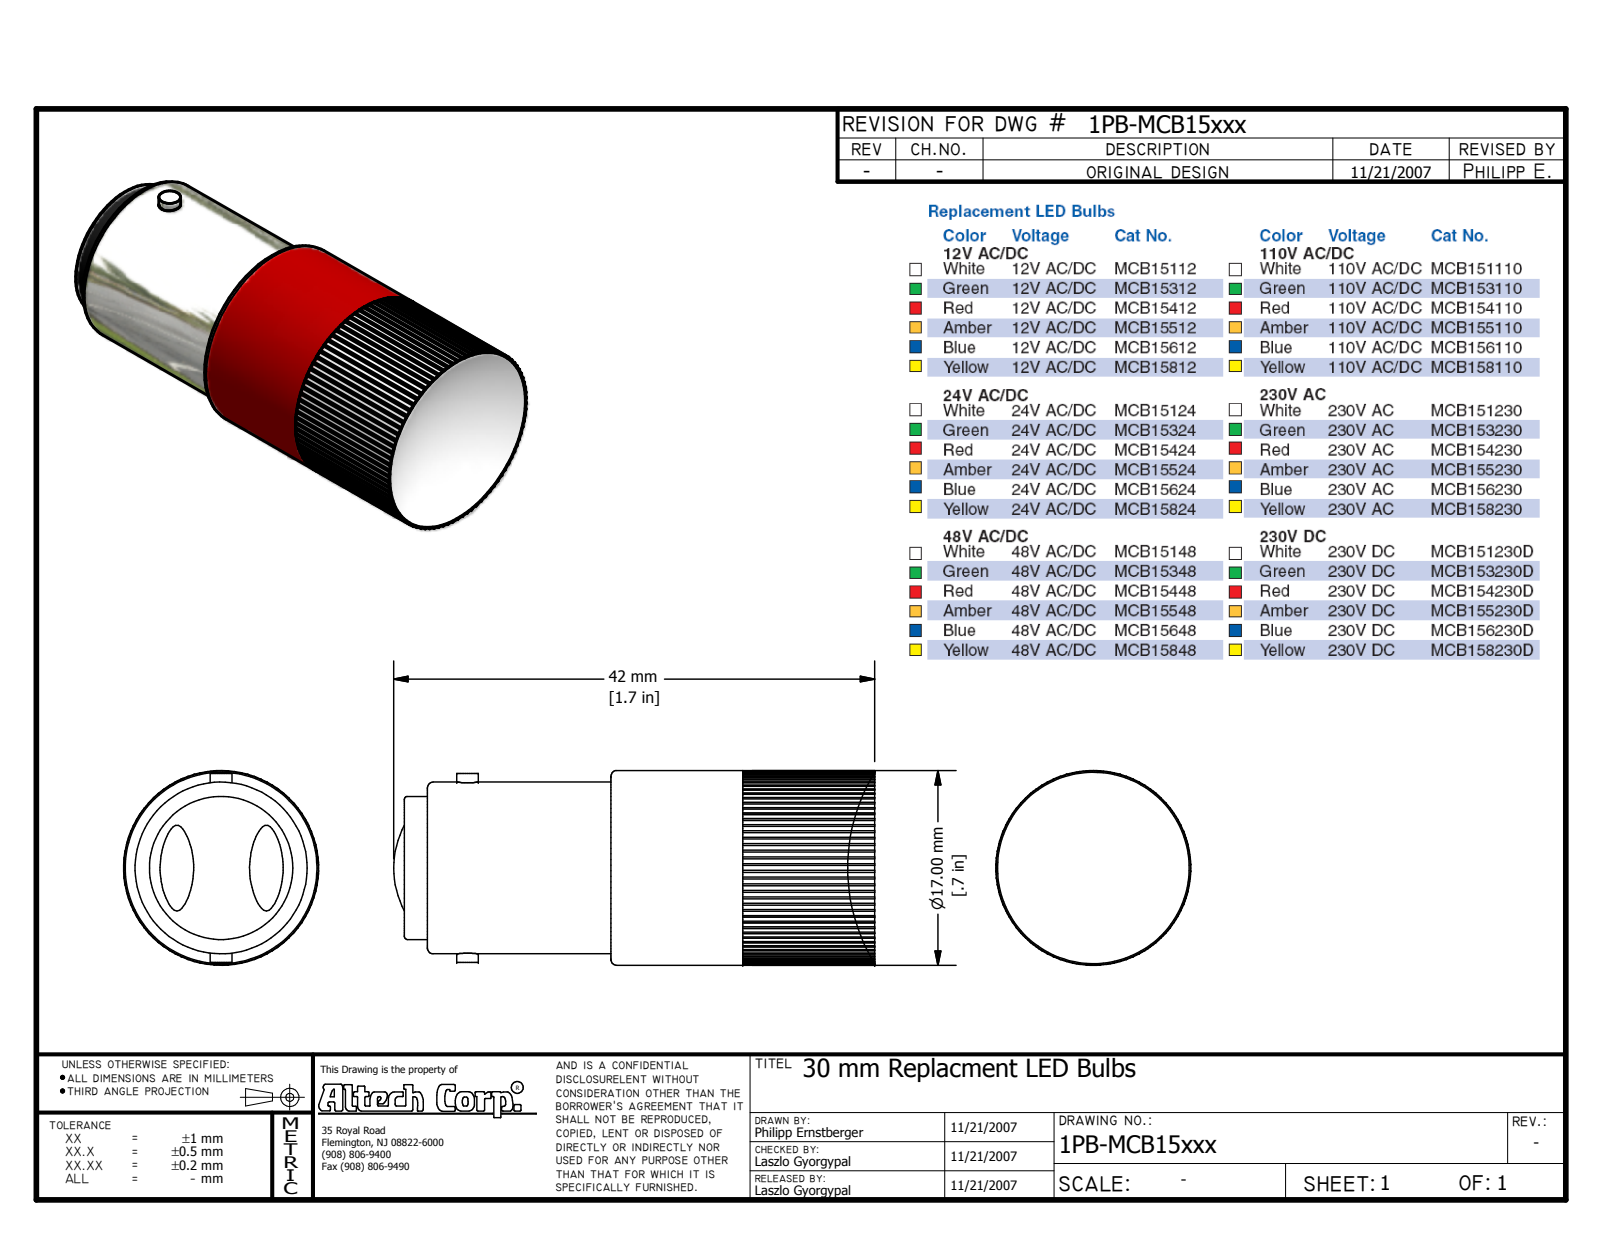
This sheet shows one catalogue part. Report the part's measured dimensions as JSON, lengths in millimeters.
{"part_name": "MCB15xyyy", "step_written_by": "Autodesk Inventor 2008 (AUTOMOTIVE_DESIGN)", "units": "millimeters", "bodies": {"solids": 1, "faces": 287, "planar": 96, "cylindrical": 185, "other": 6}, "overall_size": [41.94, 17, 17], "volume_mm3": 8018, "surface_area_mm2": 2558, "round_bosses_or_shafts": [[17, 1], [15, 1], [12.5, 1], [1.9, 1]], "partial_cylinders_radius": [[8.45, 1]], "face_to_face_distances": [2, 16, 18, 23, 39, 41, 11.5, 16.5, 27.5, 29.5]}
